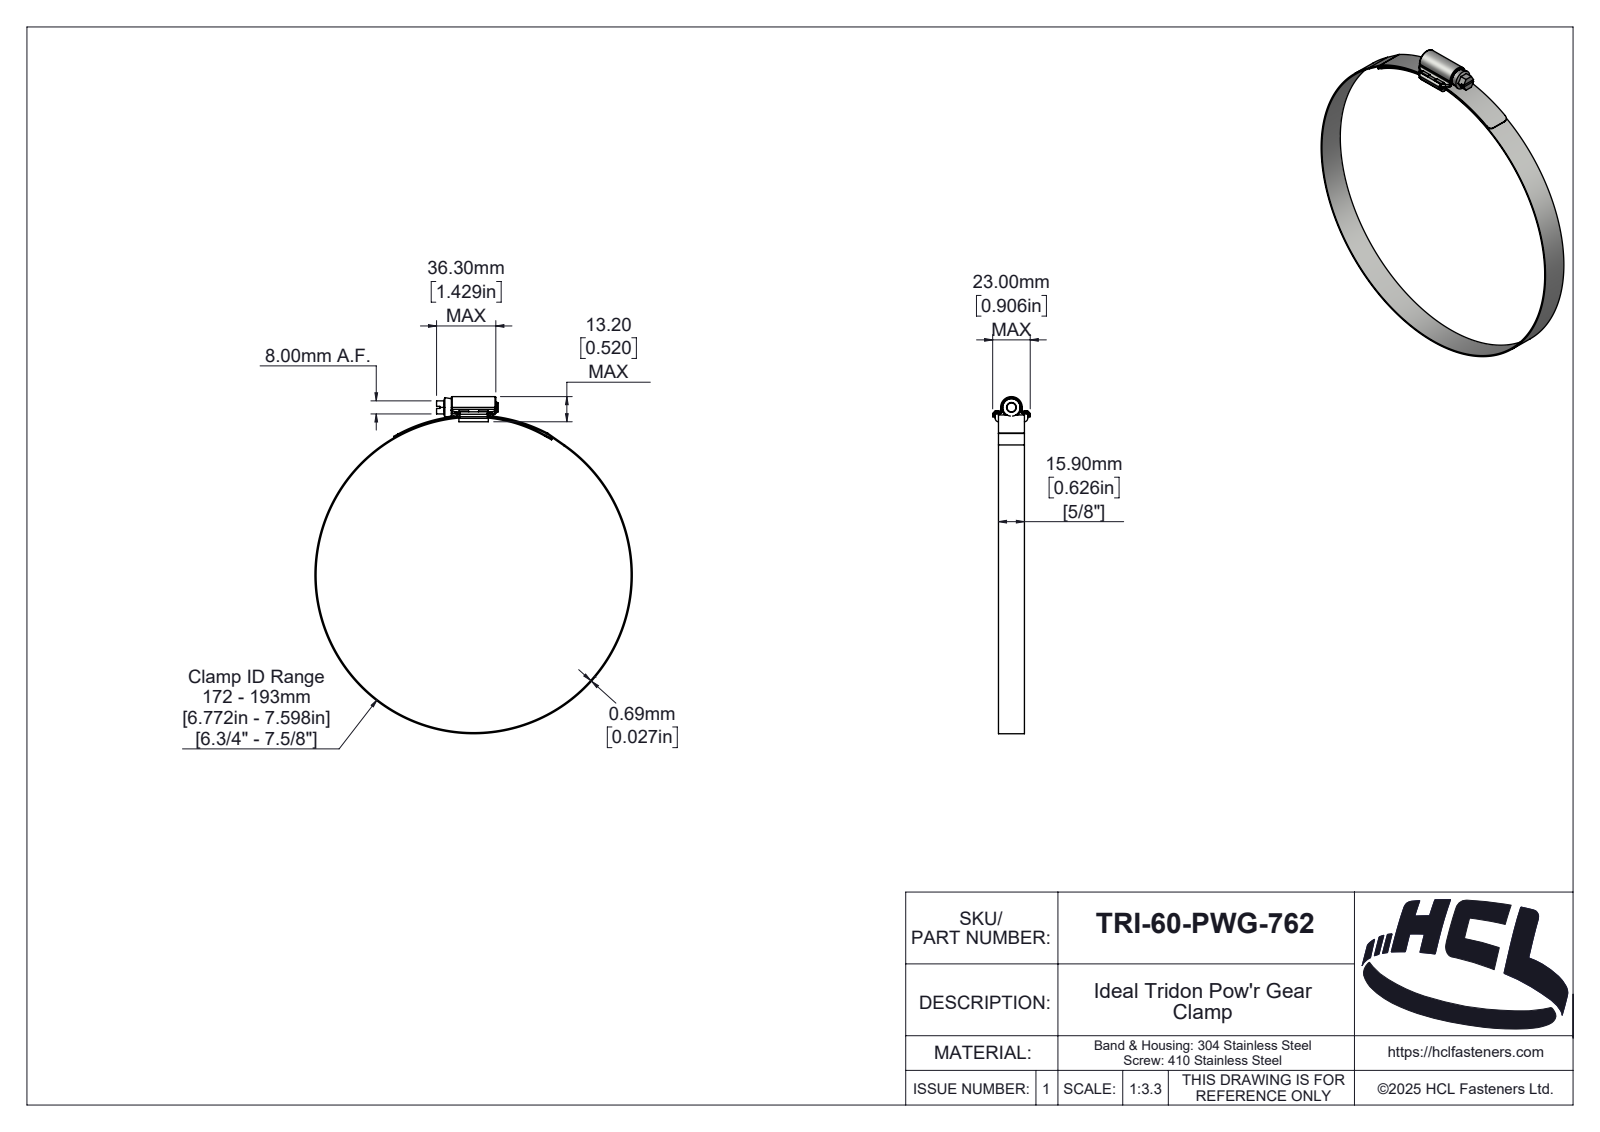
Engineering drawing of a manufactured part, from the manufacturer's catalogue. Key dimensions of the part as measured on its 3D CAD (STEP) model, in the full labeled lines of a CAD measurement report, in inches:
Part name (STEP PRODUCT): TRI-60-PWG-762
STEP written by: SolidWorks 2025 (AUTOMOTIVE_DESIGN)
Units: inches
Bodies: 4 solids, 268 faces (87 planar, 102 cylindrical, 79 other)
Overall size (bounding box): 8.126 × 7.653 × 0.906
Volume: 0.793 in³ · Surface area: 43.68 in²
Round holes (diameter × count): ⌀7.598 ×1
Round bosses / shafts (diameter × count): ⌀7.653 ×1, ⌀0.421 ×1, ⌀0.236 ×1
Partial cylindrical surfaces — rounded edges, fillets, slot ends (radius × count): R0.039 ×14, R0.02 ×4, R0.059 ×4, R0.079 ×3, R0.004 ×2, R0.083 ×2, R0.118 ×2, R0.018 ×1
Main face-to-face distances: 0.626, 0.079, 0.027, 0.705, 0.193, 0.047, 0.179, 0.132, 0.604, 0.1
